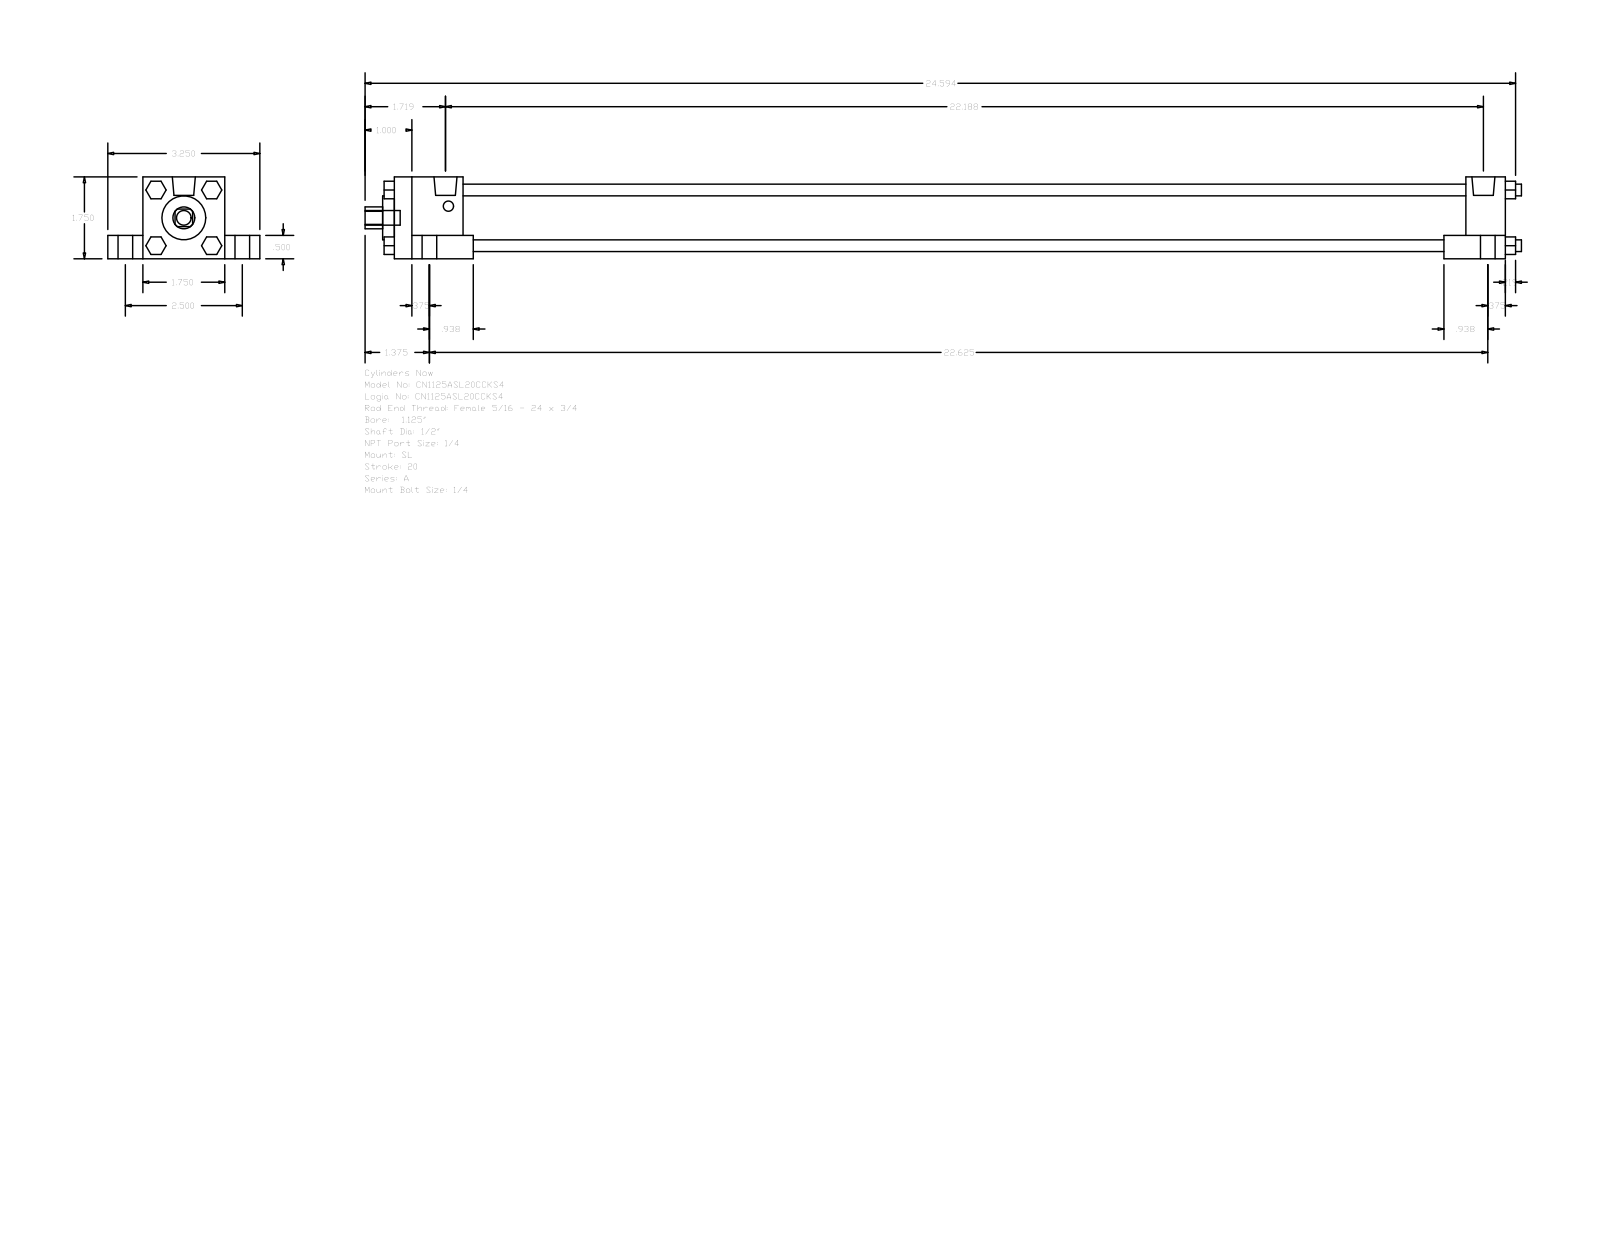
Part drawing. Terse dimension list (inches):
name: A_SL__0112_0.5
written by: GSSL Pune (CONFIG_CONTROL_DESIGN)
unit: in
bodies: 0 solids, 150 faces (114 planar, 36 cylindrical, 0 other)
size: 24.719 × 3.25 × 1.75
holes: 1× ⌀0.5, 1× ⌀0.937, 1× ⌀1.255
bosses: 5× ⌀0.313, 4× ⌀0.563, 4× ⌀0.25, 4× ⌀0.219, 2× ⌀0.492
rounds: 1× R0.234
face distances: 1.75, 1.25, 0.5, 0.75, 2.5, 22.281, 23.75, 22.906, 0.844, 1.469
